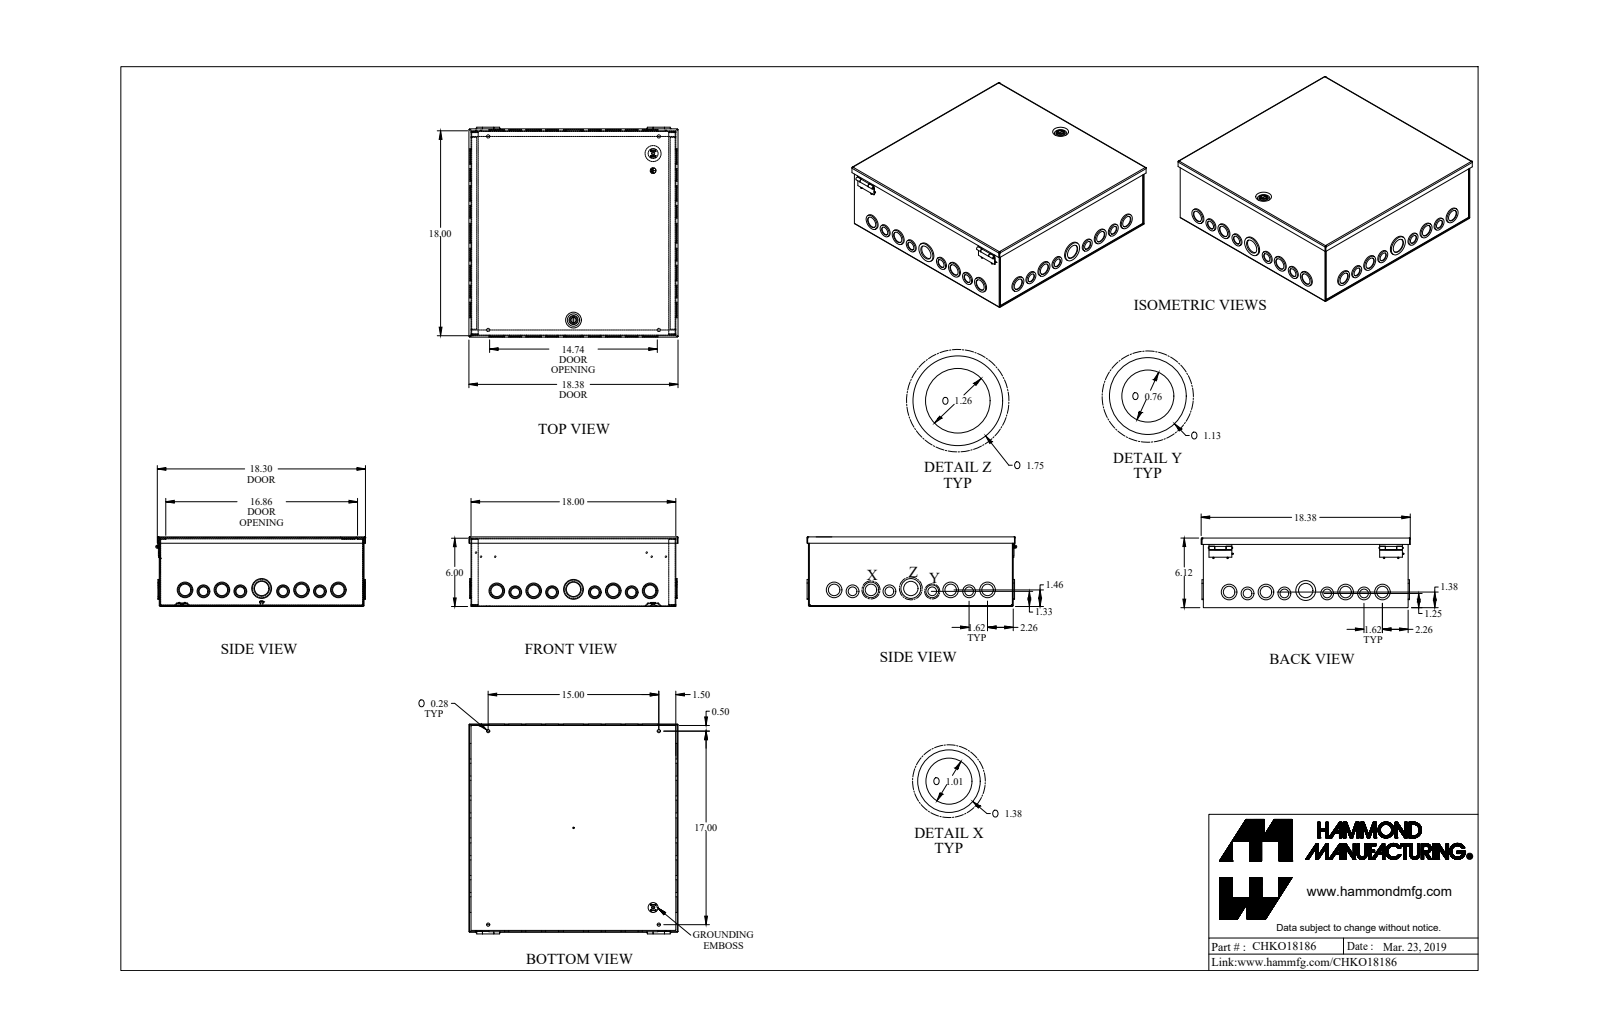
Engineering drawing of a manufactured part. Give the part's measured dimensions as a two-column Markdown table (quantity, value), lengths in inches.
| quantity | value |
| --- | --- |
| part name | CHKO18186_Default |
| STEP written by | SolidWorks 2019 (CONFIG_CONTROL_DESIGN) |
| units | inches |
| bodies | 12 solids, 919 faces (416 planar, 460 cylindrical, 43 other) |
| overall size | 18.443 × 18.38 × 6.118 |
| volume | 69.62 in³ |
| surface area | 2 453 in² |
| round holes (diameter × count) | 1.011 × 16, 1.261 × 10, 0.761 × 8, 0.281 × 4, 1.636 × 2, 0.125 × 1, 0.17 × 1, 0.319 × 1, 0.476 × 1, 0.5 × 1 |
| round bosses / shafts (diameter × count) | 1.125 × 14, 0.875 × 8, 0.131 × 8, 1.375 × 7, 0.875 × 6, 1.125 × 4, 1.375 × 3, 1.75 × 2 |
| partial cylindrical surfaces (radius × count) | 0.029 × 16, 0.086 × 16, 0.057 × 8, 0.012 × 4, 0.1 × 4, 0.036 × 2, 0.079 × 2, 0.25 × 2 |
| main face-to-face distances | 0.057, 6.061, 17.943, 6.118, 6.004, 18, 17.886, 5.943, 0.118, 0.08 |
| hole center spacings | 1.625, 3.24, 8.621, 7, 10.24, 1.896, 3.502, 4.862 |
